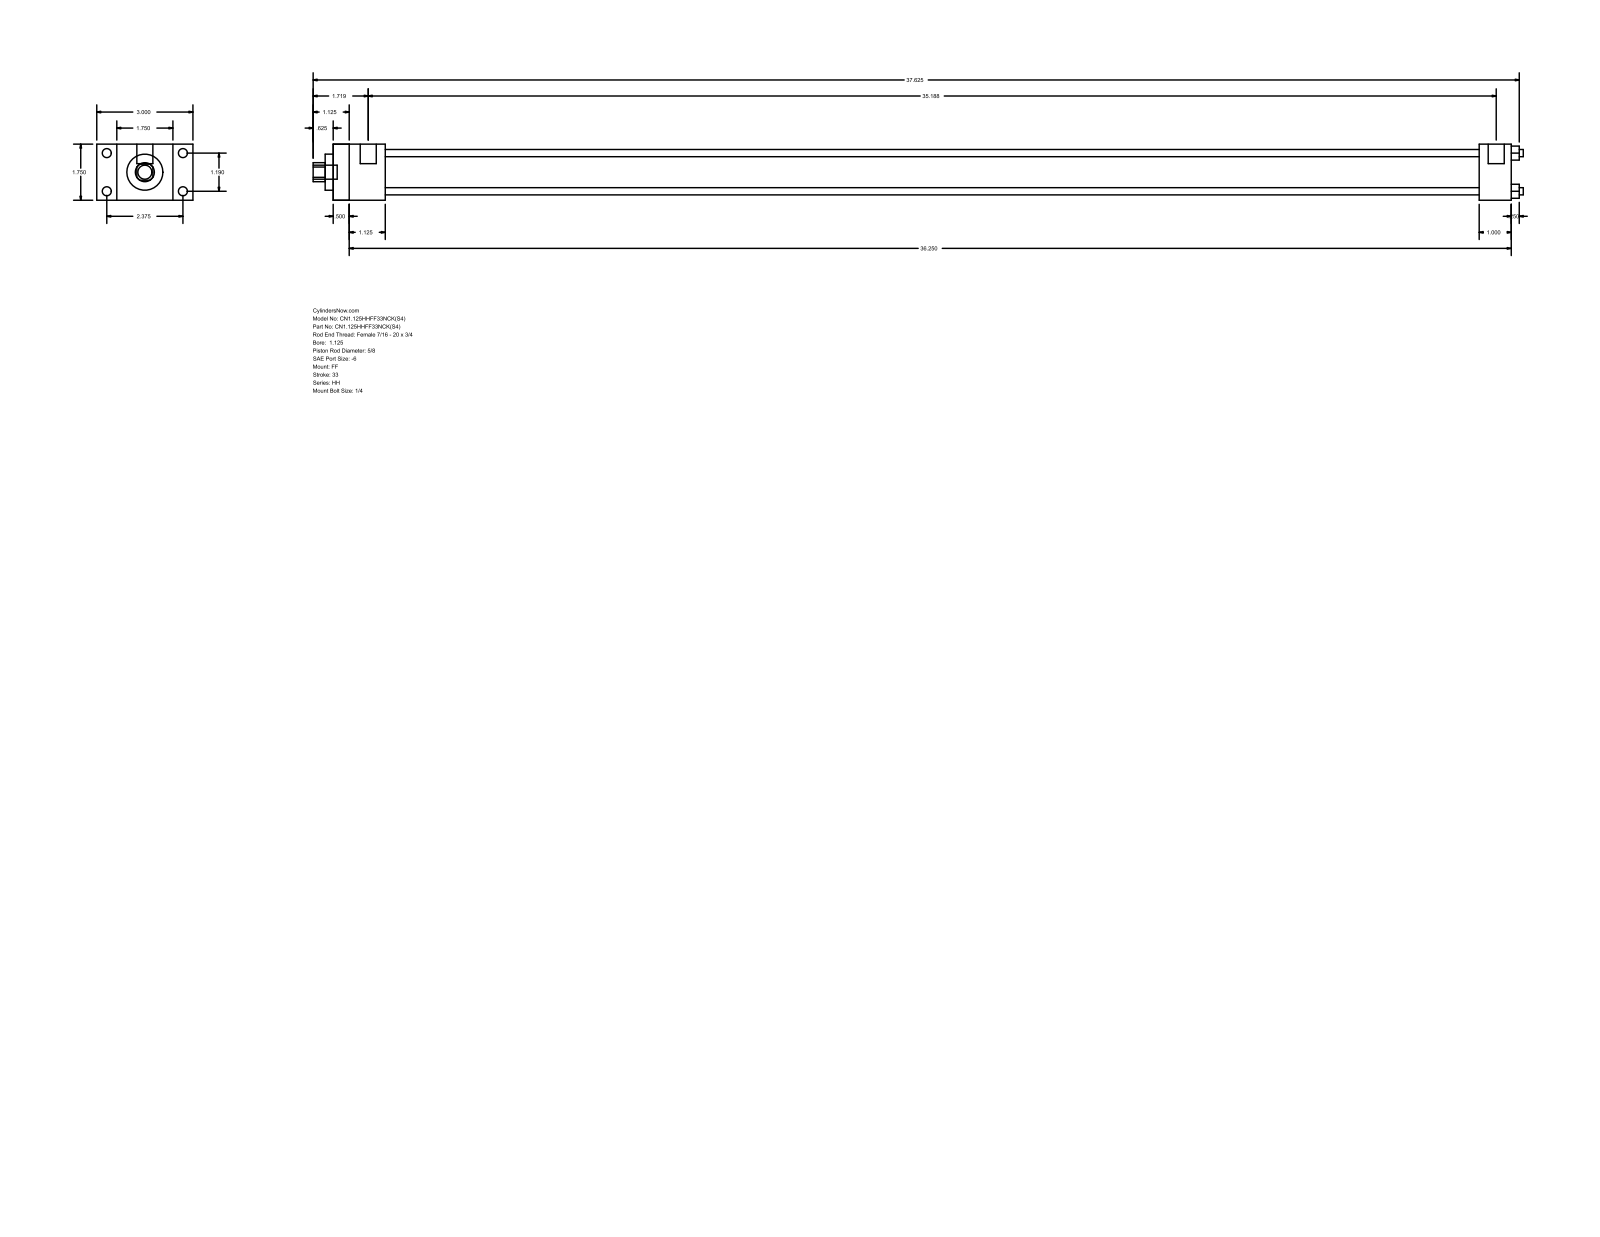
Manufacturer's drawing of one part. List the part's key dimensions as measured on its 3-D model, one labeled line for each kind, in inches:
Part name (STEP PRODUCT): HH_FF__0112_0.625
STEP written by: GSSL Pune (CONFIG_CONTROL_DESIGN)
Units: inches
Bodies: 0 solids, 92 faces (64 planar, 28 cylindrical, 0 other)
Overall size (bounding box): 37.75 × 3 × 1.75
Round holes (diameter × count): ⌀0.225 ×4, ⌀0.625 ×1, ⌀1.125 ×1, ⌀1.375 ×1
Round bosses / shafts (diameter × count): ⌀0.281 ×4, ⌀0.219 ×4, ⌀0.5 ×2, ⌀0.437 ×1
Partial cylindrical surfaces — rounded edges, fillets, slot ends (radius × count): R0.297 ×1
Main face-to-face distances: 1.75, 36.75, 0.625, 0.5, 36.25, 2.375, 1.125, 1.625, 35.75, 35.25
Hole centre spacings: 0.841, 1.19, 1.683
